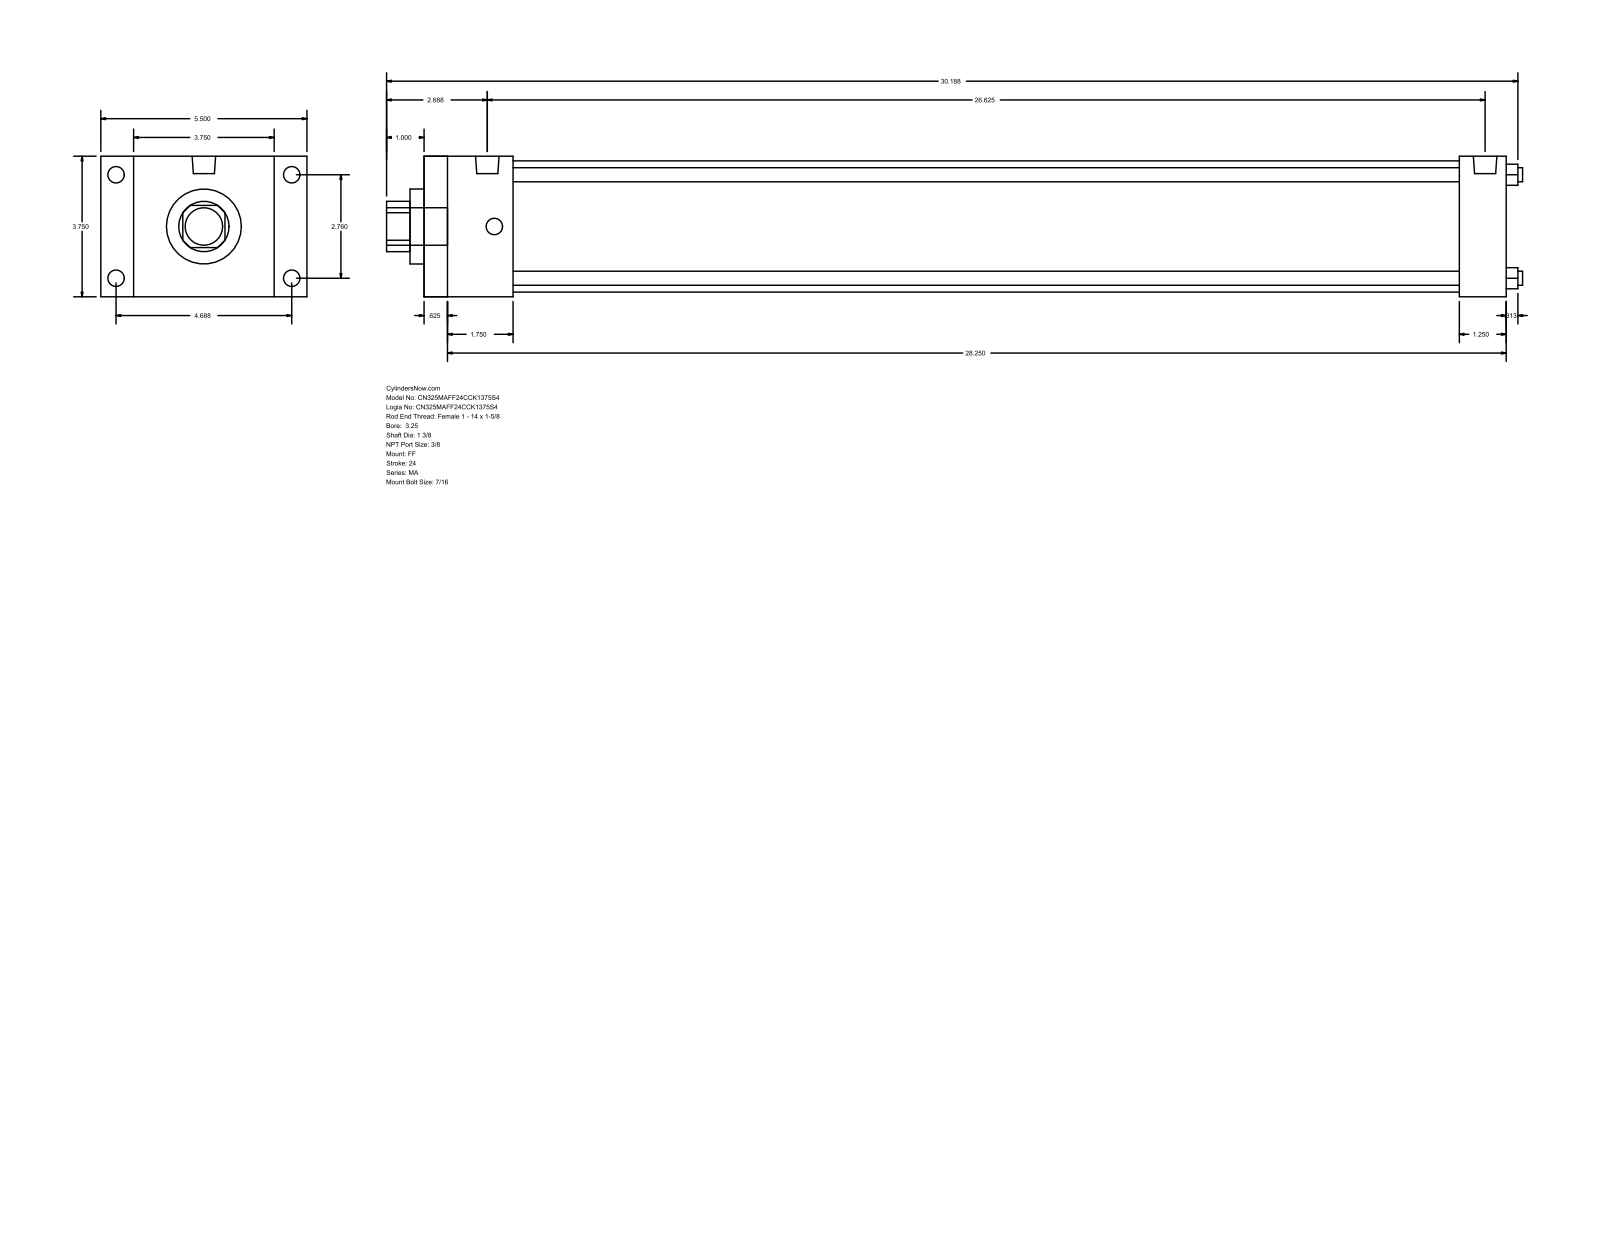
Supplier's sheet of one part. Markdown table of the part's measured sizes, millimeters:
| quantity | value |
| --- | --- |
| part name | MA_FF__0325_1.375 |
| STEP written by | GSSL Pune (CONFIG_CONTROL_DESIGN) |
| units | millimeters |
| bodies | 0 solids, 92 faces (64 planar, 28 cylindrical, 0 other) |
| overall size | 769.94 × 139.7 × 95.25 |
| round holes (diameter × count) | 9.53 × 4, 34.92 × 1, 50.8 × 1, 88.9 × 1 |
| round bosses / shafts (diameter × count) | 11.11 × 8, 15.93 × 2, 25.4 × 1 |
| partial cylindrical surfaces (radius × count) | 17.06 × 1 |
| main face-to-face distances | 95.24, 733.43, 15.87, 717.56, 22.23, 117.47, 60.32, 701.68, 44.45, 685.81 |
| hole center spacings | 49.57, 70.1, 99.14 |
